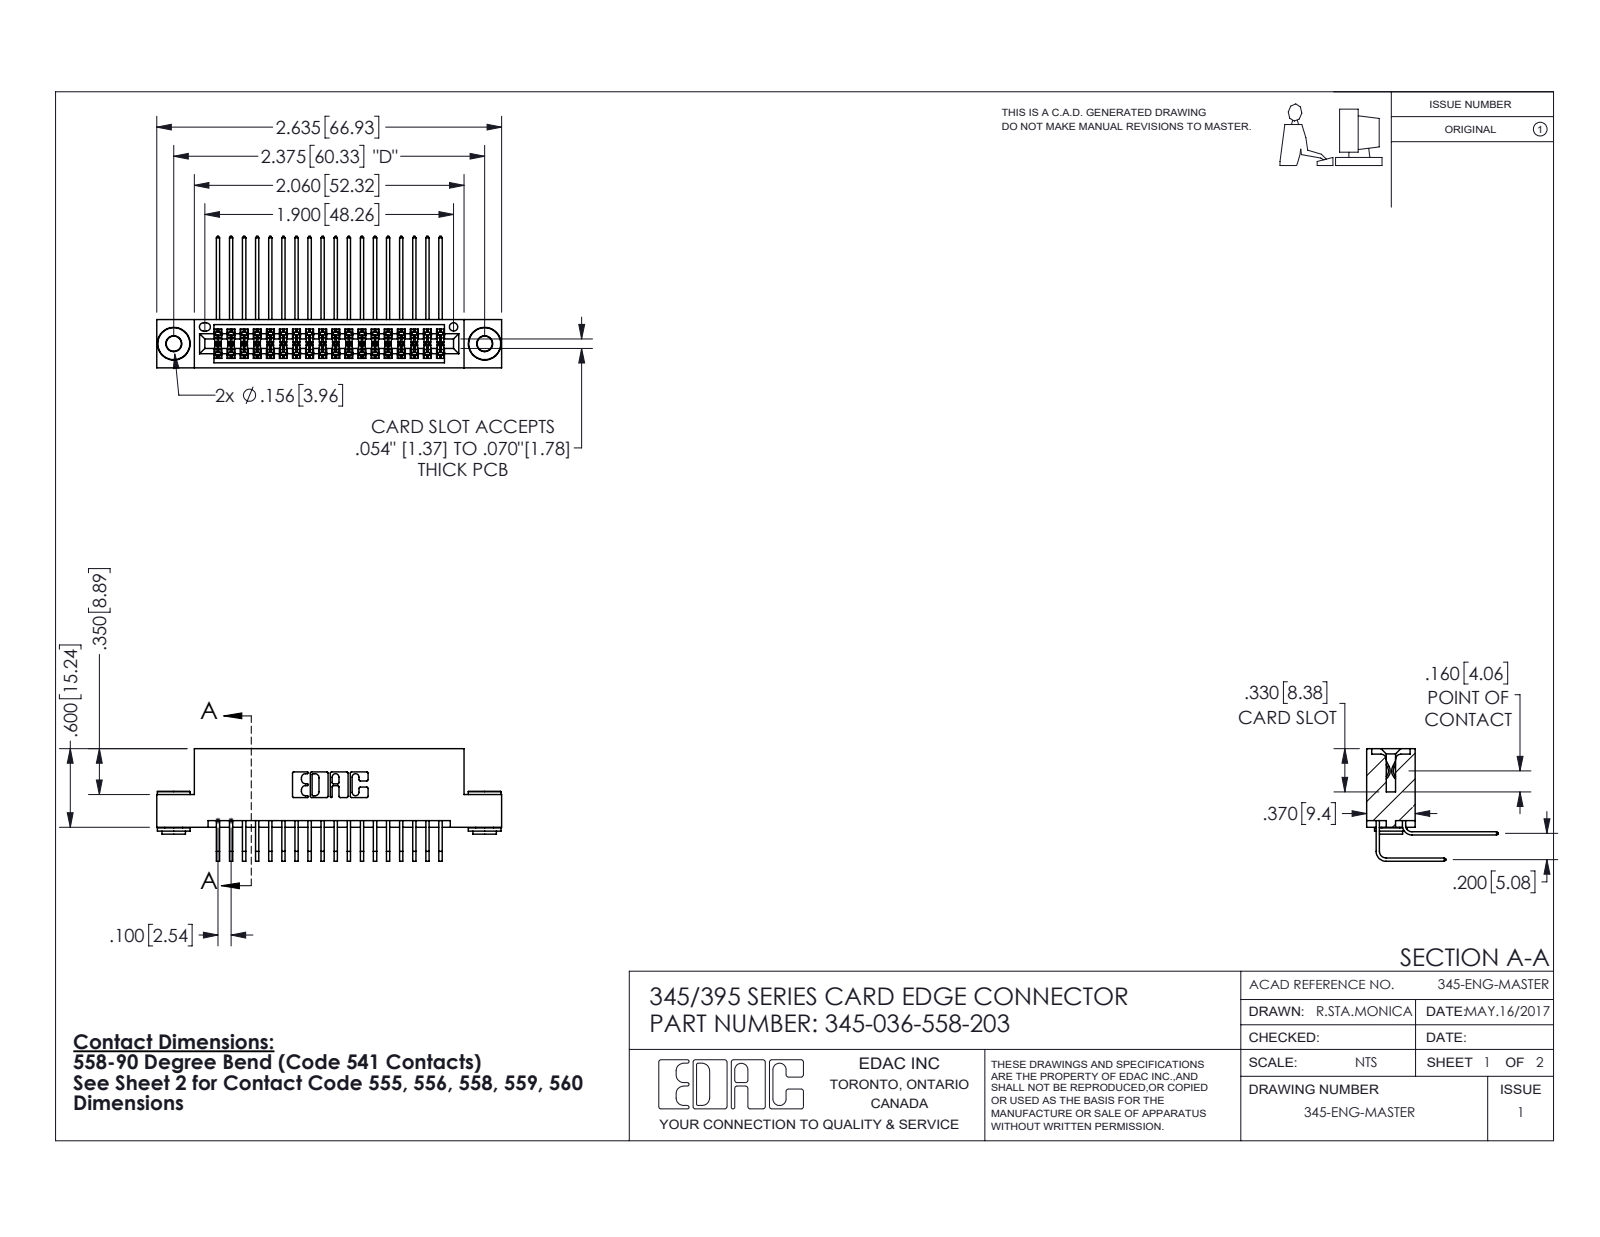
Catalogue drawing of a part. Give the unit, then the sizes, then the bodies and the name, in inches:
Units: inches
Overall size (bounding box): 2.635 × 1.005 × 0.859
Round holes (diameter × count): ⌀0.116 ×2, ⌀0.156 ×2, ⌀0.064 ×1
Round bosses / shafts (diameter × count): ⌀0.25 ×2, ⌀0.18 ×2, ⌀0.136 ×2
Partial cylindrical surfaces — rounded edges, fillets, slot ends (radius × count): R0.006 ×72, R0.01 ×22, R0.007 ×6, R0.031 ×6, R0.026 ×3, R0.014 ×2, R0.019 ×2, R0.022 ×2
Main face-to-face distances: 0.2, 0.072, 0.298, 0.37, 0.025, 0.098, 0.272, 0.225, 0.285, 0.025
Hole centre spacings: 0.27, 2.141, 2.375
Volume: 0.397 in³ · Surface area: 16.02 in²
Bodies: 39 solids, 2036 faces (1350 planar, 678 cylindrical, 8 other)
Part name (STEP PRODUCT): 345-036-558-203; 345-292-001_558 559 Tail - 1; 345 Part_Flush Mounting Lugs - 0.156 Dia-TH; 345-250-002_345-250-002-102 (+1 more)
STEP written by: SolidWorks 2016 (CONFIG_CONTROL_DESIGN)
